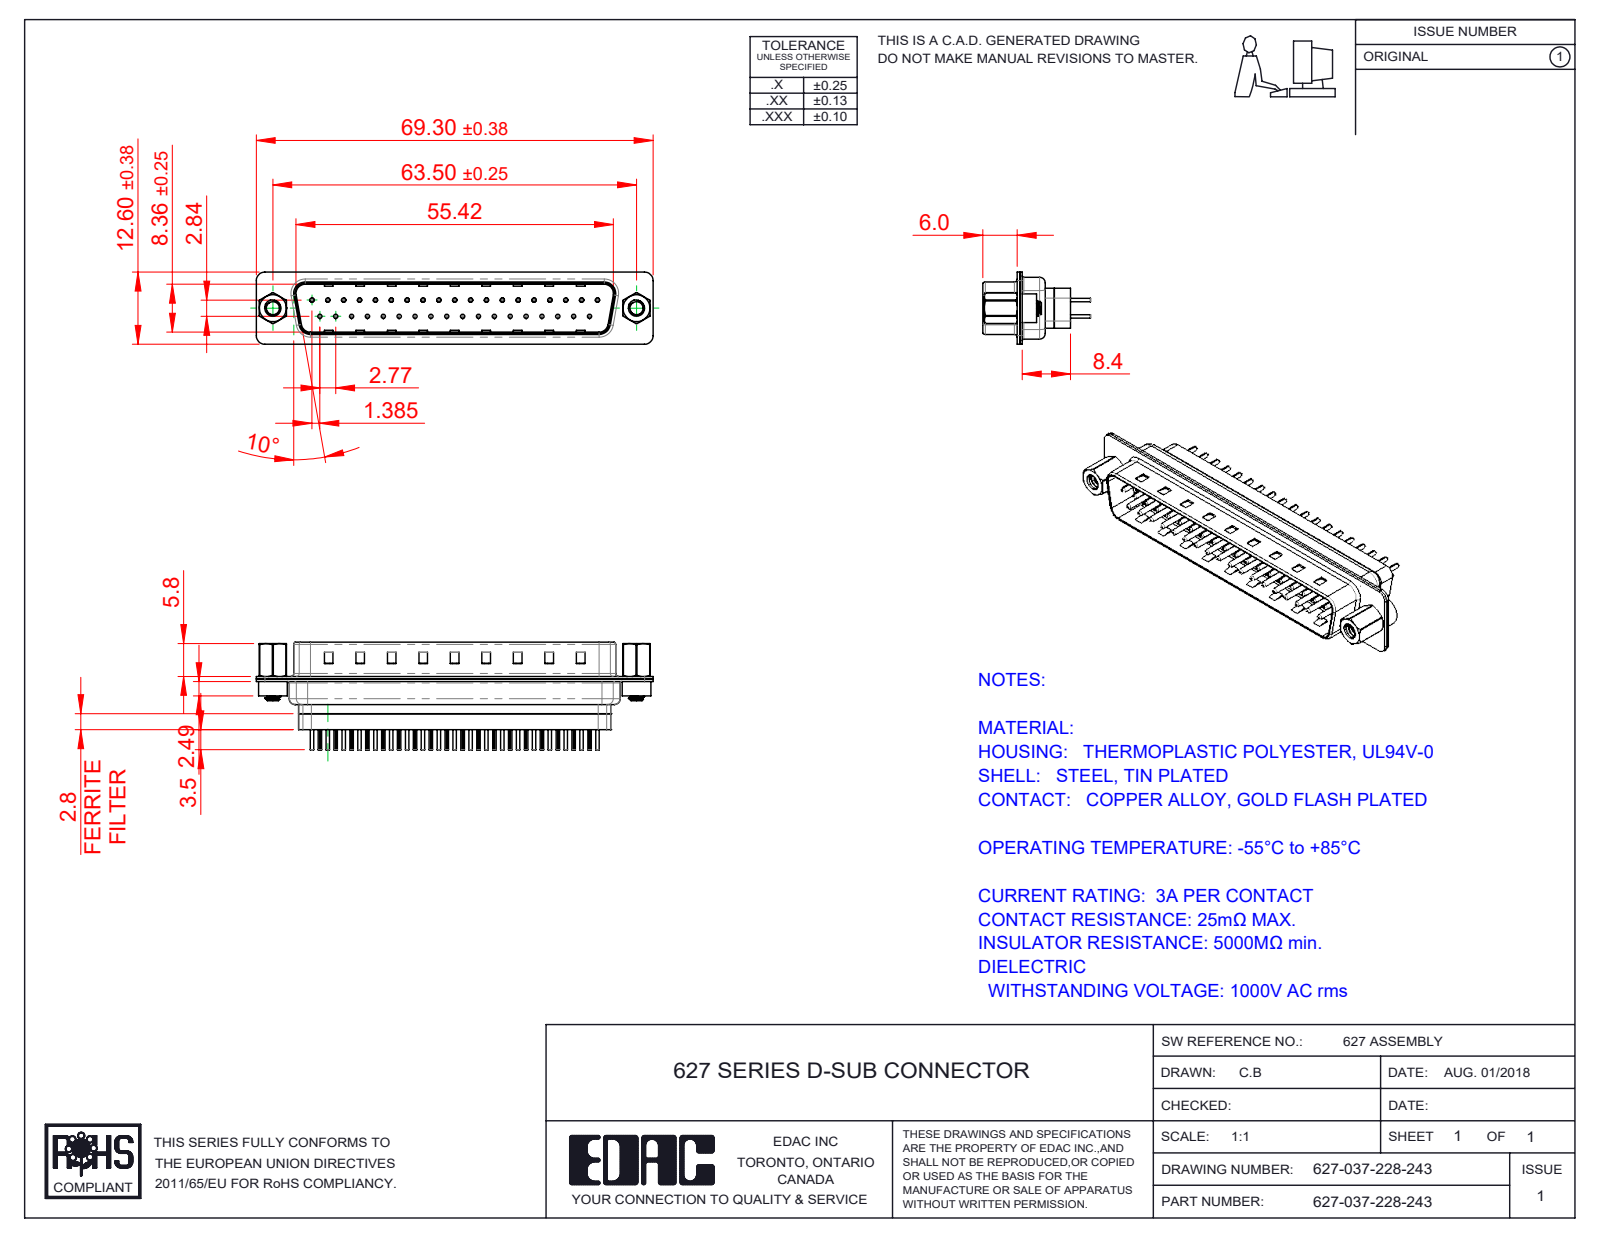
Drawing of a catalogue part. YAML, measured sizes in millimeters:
part_name: "627 Shell Rear_37 Contacts; 627 4-40 Hex Standoff; 627-037-228-043; 627 Housing_37 FF (+4 more)"
step_written_by: "SolidWorks 2020 (CONFIG_CONTROL_DESIGN)"
units: millimeters
bodies: {solids: 45, faces: 4245, planar: 1119, cylindrical: 1659, other: 1467}
overall_size: [69.3, 18.8, 12.6]
volume: 4764
surface_area: 12768
round_holes:
  - {diameter: 0.2, count: 37}
  - {diameter: 0.35, count: 37}
  - {diameter: 1.1, count: 37}
  - {diameter: 1.6, count: 37}
  - {diameter: 2.26, count: 2}
  - {diameter: 2.29, count: 2}
  - {diameter: 4, count: 2}
  - {diameter: 4.8, count: 2}
round_bosses_or_shafts:
  - {diameter: 2, count: 37}
  - {diameter: 1.5, count: 37}
  - {diameter: 0.75, count: 37}
  - {diameter: 0.6, count: 37}
  - {diameter: 5, count: 2}
  - {diameter: 4.9, count: 2}
  - {diameter: 2.79, count: 2}
partial_cylinders:
  - {radius: 0.1, count: 74}
  - {radius: 1.5, count: 16}
  - {radius: 2, count: 12}
  - {radius: 0.5, count: 8}
  - {radius: 1.6, count: 8}
  - {radius: 0.25, count: 4}
  - {radius: 0.6, count: 4}
  - {radius: 0.65, count: 4}
face_to_face_distances: [0.4, 6.05, 0.82, 9.58, 0.45, 8.4, 0.68, 7.68, 1.5, 1.08]
hole_center_spacings: [3.16, 2.77, 5.54, 8.31, 5.04, 10.1, 11.08, 12.78]
